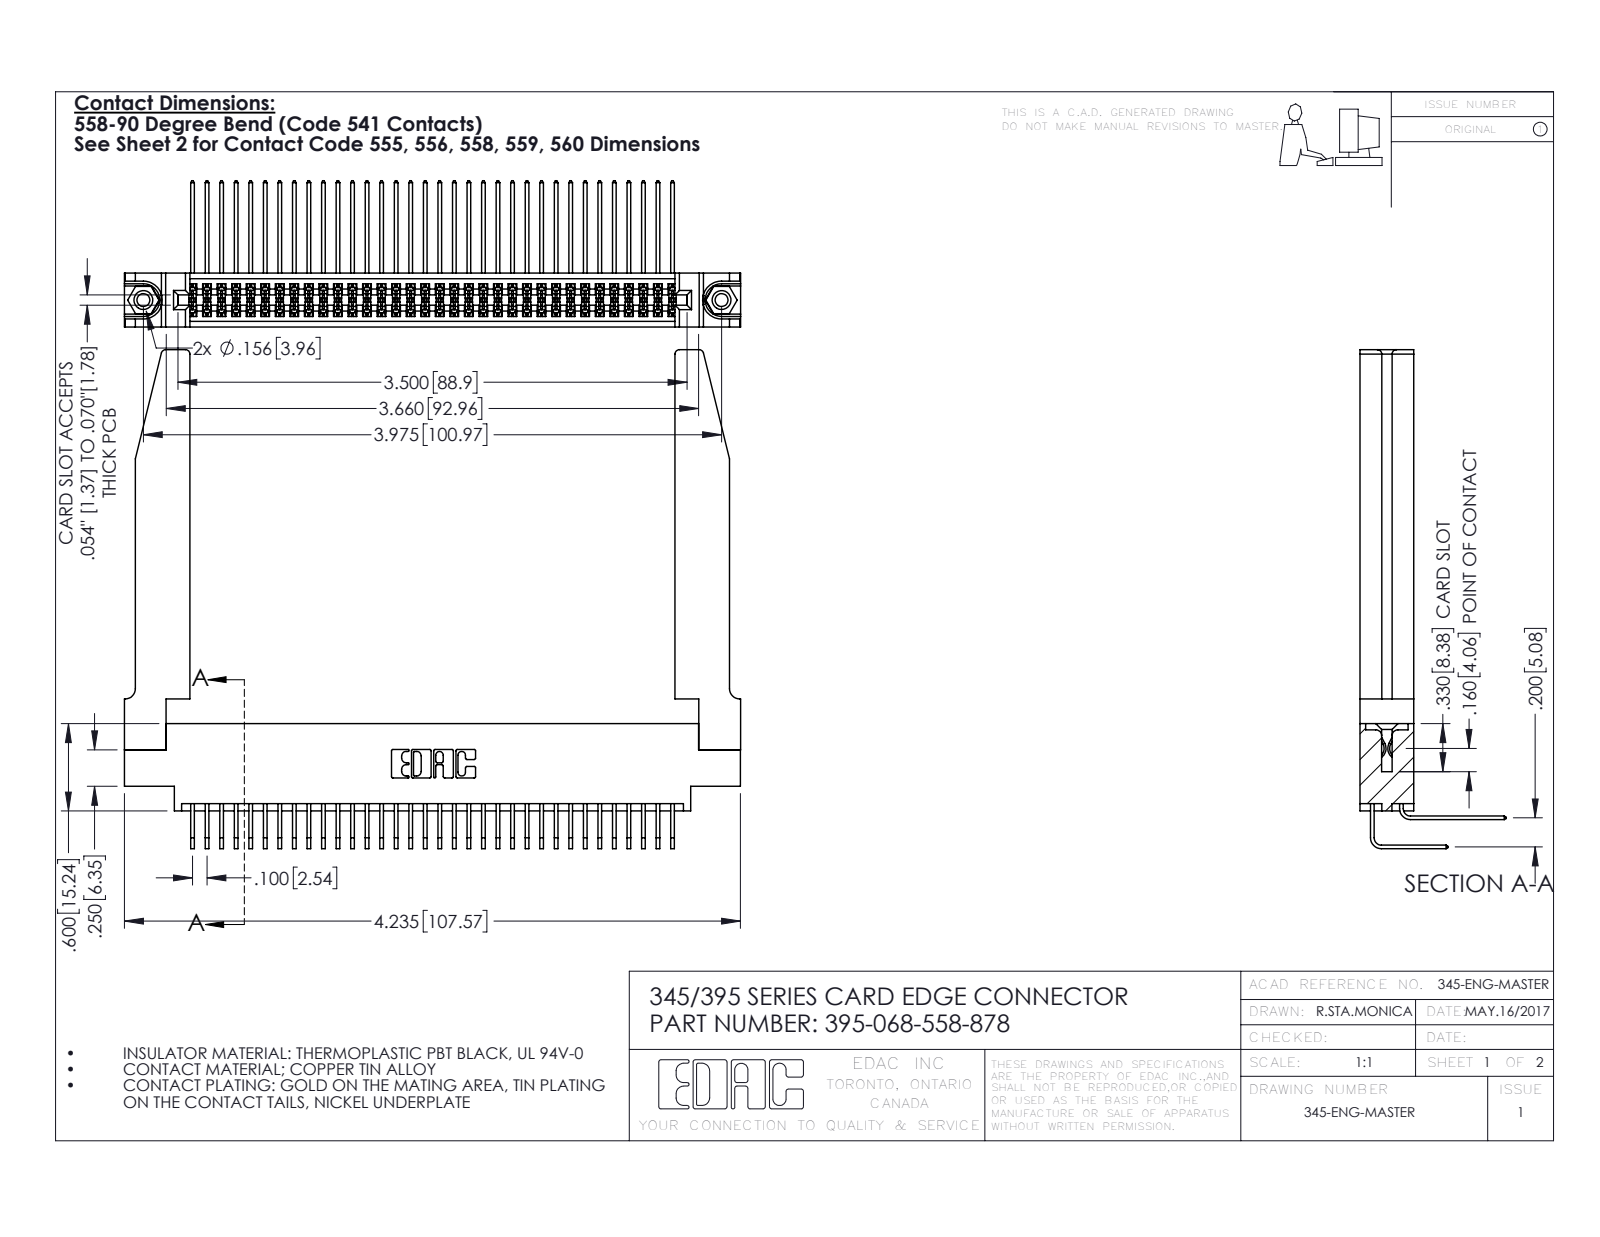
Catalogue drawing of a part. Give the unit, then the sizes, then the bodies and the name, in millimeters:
Units: millimetres
Overall size (bounding box): 107.6 × 87.1 × 25.5
Round holes (diameter × count): ⌀2.3 ×2, ⌀3.2 ×2, ⌀4 ×2, ⌀1.6 ×1
Round bosses / shafts (diameter × count): ⌀3.9 ×2
Partial cylindrical surfaces — rounded edges, fillets, slot ends (radius × count): R0.2 ×103, R0.3 ×22, R0.8 ×8, R0.2 ×6, R0.8 ×6, R0.7 ×3, R0.4 ×2, R0.5 ×2
Main face-to-face distances: 9.4, 1.8, 7.6, 5.1, 2.5, 6.9, 0.6, 5.7, 3.8, 3.8
Hole centre spacings: 6.9, 95, 101
Volume: 18 420 mm³ · Surface area: 24 430 mm²
Bodies: 73 solids, 3900 faces (2606 planar, 1242 cylindrical, 52 other)
Part name (STEP PRODUCT): 345-220-078_345-220-078; 345-250-001_345-250-001-102; 345-292-001_558 Tail - 2; 345-292-001_558 559 Tail - 1 (+2 more)
STEP written by: SolidWorks 2016 (CONFIG_CONTROL_DESIGN)
